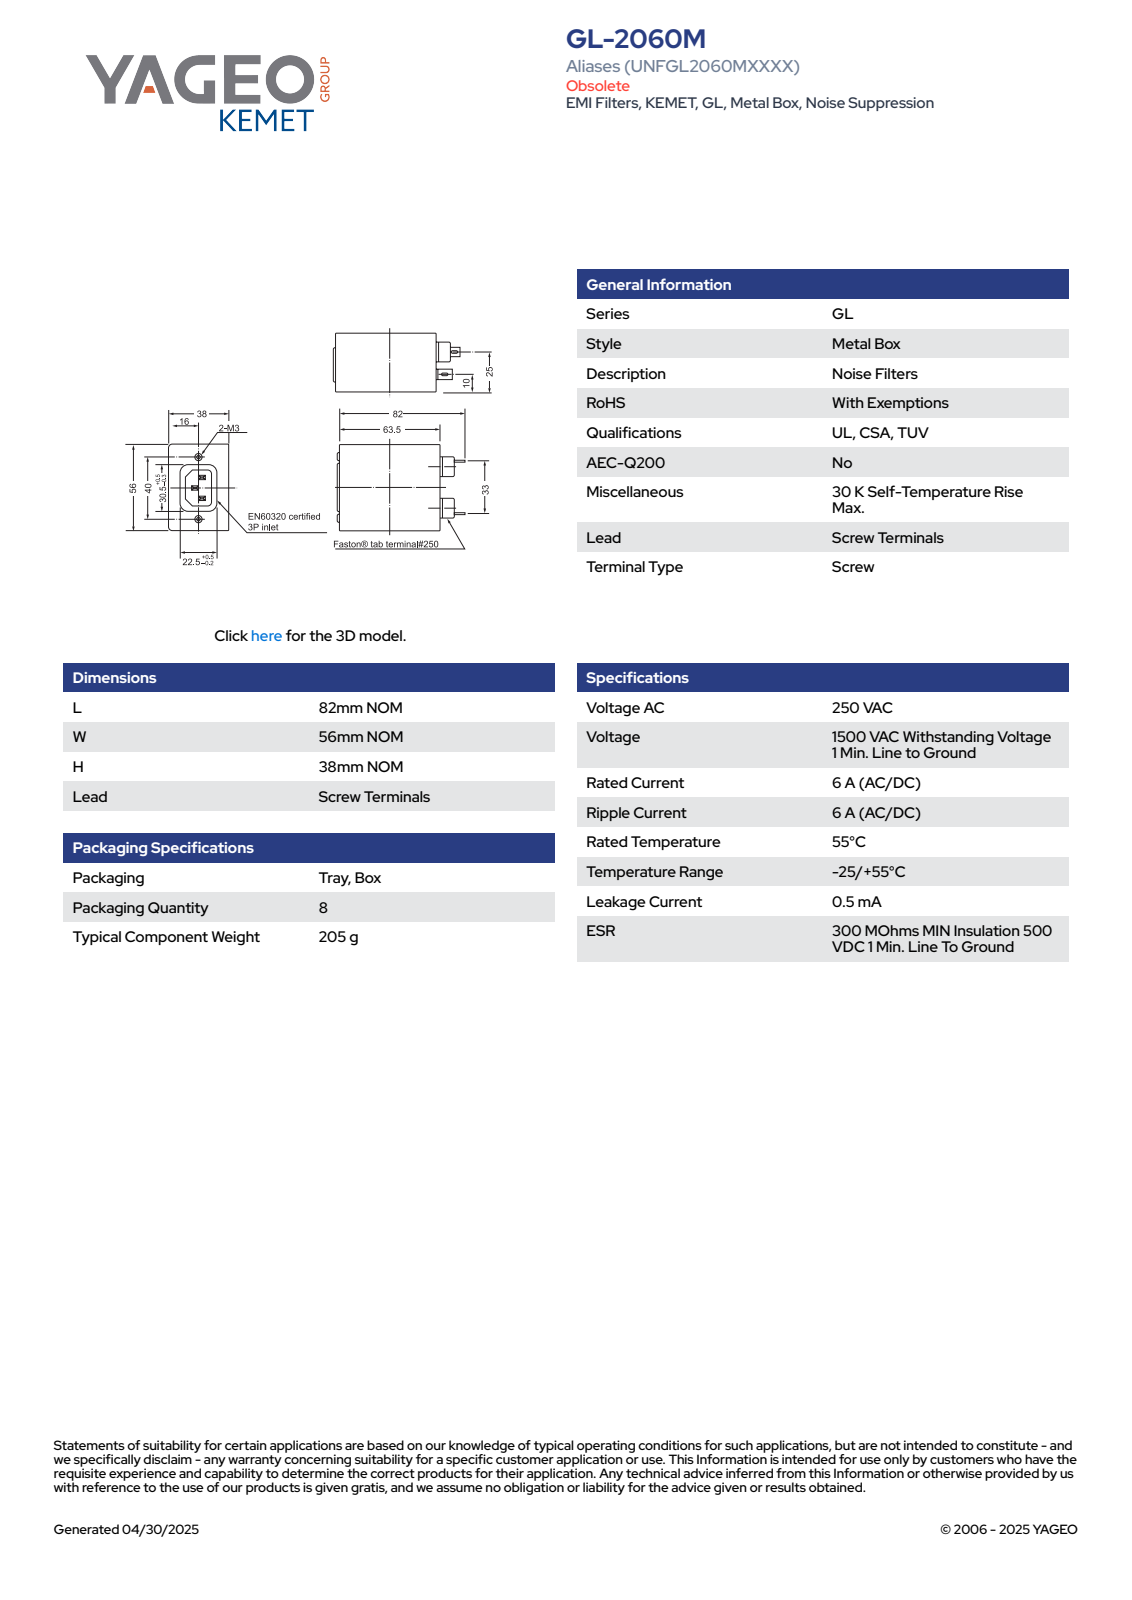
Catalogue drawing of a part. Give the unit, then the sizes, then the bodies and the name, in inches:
Units: inches
Overall size (bounding box): 3.228 × 2.205 × 1.496
Round holes (diameter × count): ⌀0.118 ×2
Partial cylindrical surfaces — rounded edges, fillets, slot ends (radius × count): R0.02 ×24, R0.039 ×10, R0.118 ×8, R0.059 ×2
Main face-to-face distances: 1.496, 2.205, 2.5, 0.591, 0.512, 0.276, 1.909, 1.614, 0.846, 0.984
Hole centre spacings: 1.575
Volume: 7.887 in³ · Surface area: 28.8 in²
Bodies: 1 solid, 206 faces (123 planar, 63 cylindrical, 20 other)
Part name (STEP PRODUCT): ENF_KGLM_L82W56H38
STEP written by: SolidWorks 2014 (AUTOMOTIVE_DESIGN)
